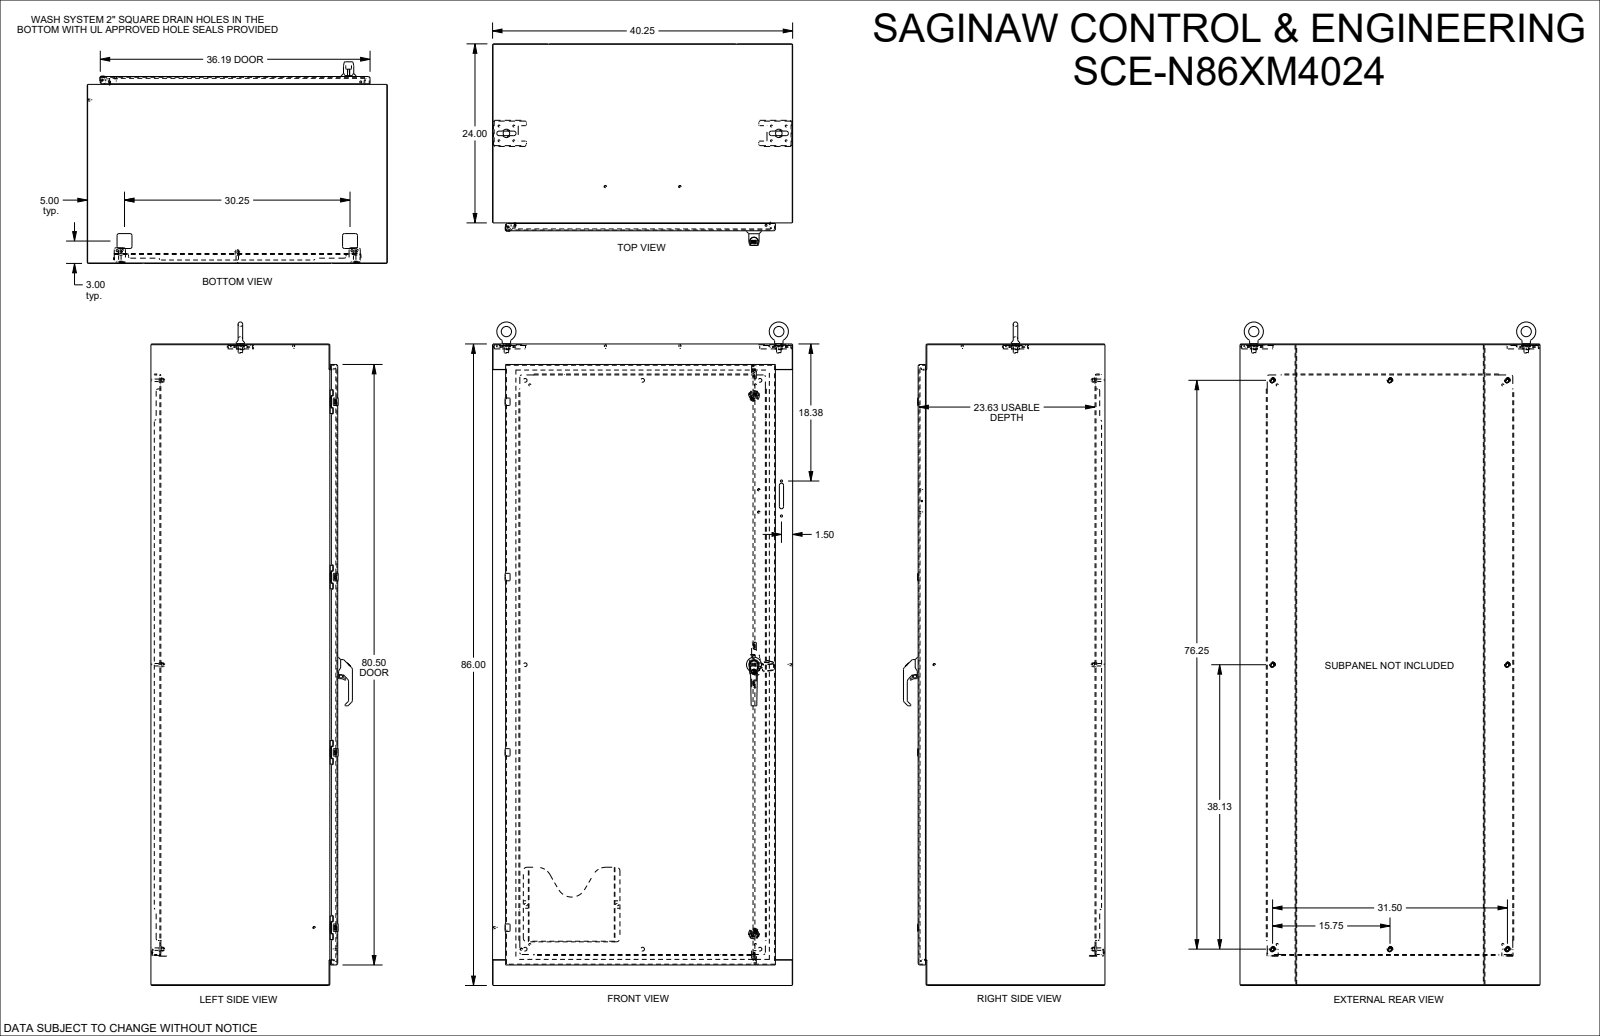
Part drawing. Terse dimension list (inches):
name: SCE-N86XM4024
written by: SolidWorks 2023 (AUTOMOTIVE_DESIGN)
unit: in
bodies: 22 solids, 3144 faces (1331 planar, 1025 cylindrical, 788 other)
size: 88.945 × 40.25 × 27.046
volume: 1 459 in³; area: 27 936 in²
holes: 10× ⌀0.25, 8× ⌀0.205, 8× ⌀0.244, 8× ⌀0.375, 4× ⌀0.04, 4× ⌀0.17, 4× ⌀0.218, 4× ⌀0.256, 2× ⌀0.281, 2× ⌀0.343, 2× ⌀0.36, 2× ⌀0.875
bosses: 12× ⌀0.17, 8× ⌀0.25, 8× ⌀0.24, 5× ⌀0.196, 2× ⌀1.4, 2× ⌀1.173, 2× ⌀0.6, 2× ⌀0.341
rounds: 96× R0.03, 68× R0.015, 37× R0.04, 31× R0.125, 24× R0.02, 24× R0.063, 22× R0.039, 21× R0.079
face distances: 0.104, 24.954, 0.104, 40.146, 24.85, 25.058, 40.25, 40.042, 85.896, 23.896
hole spacings: 23.5, 47, 0.493, 0.494, 0.984, 1.399, 1.4, 1.979
